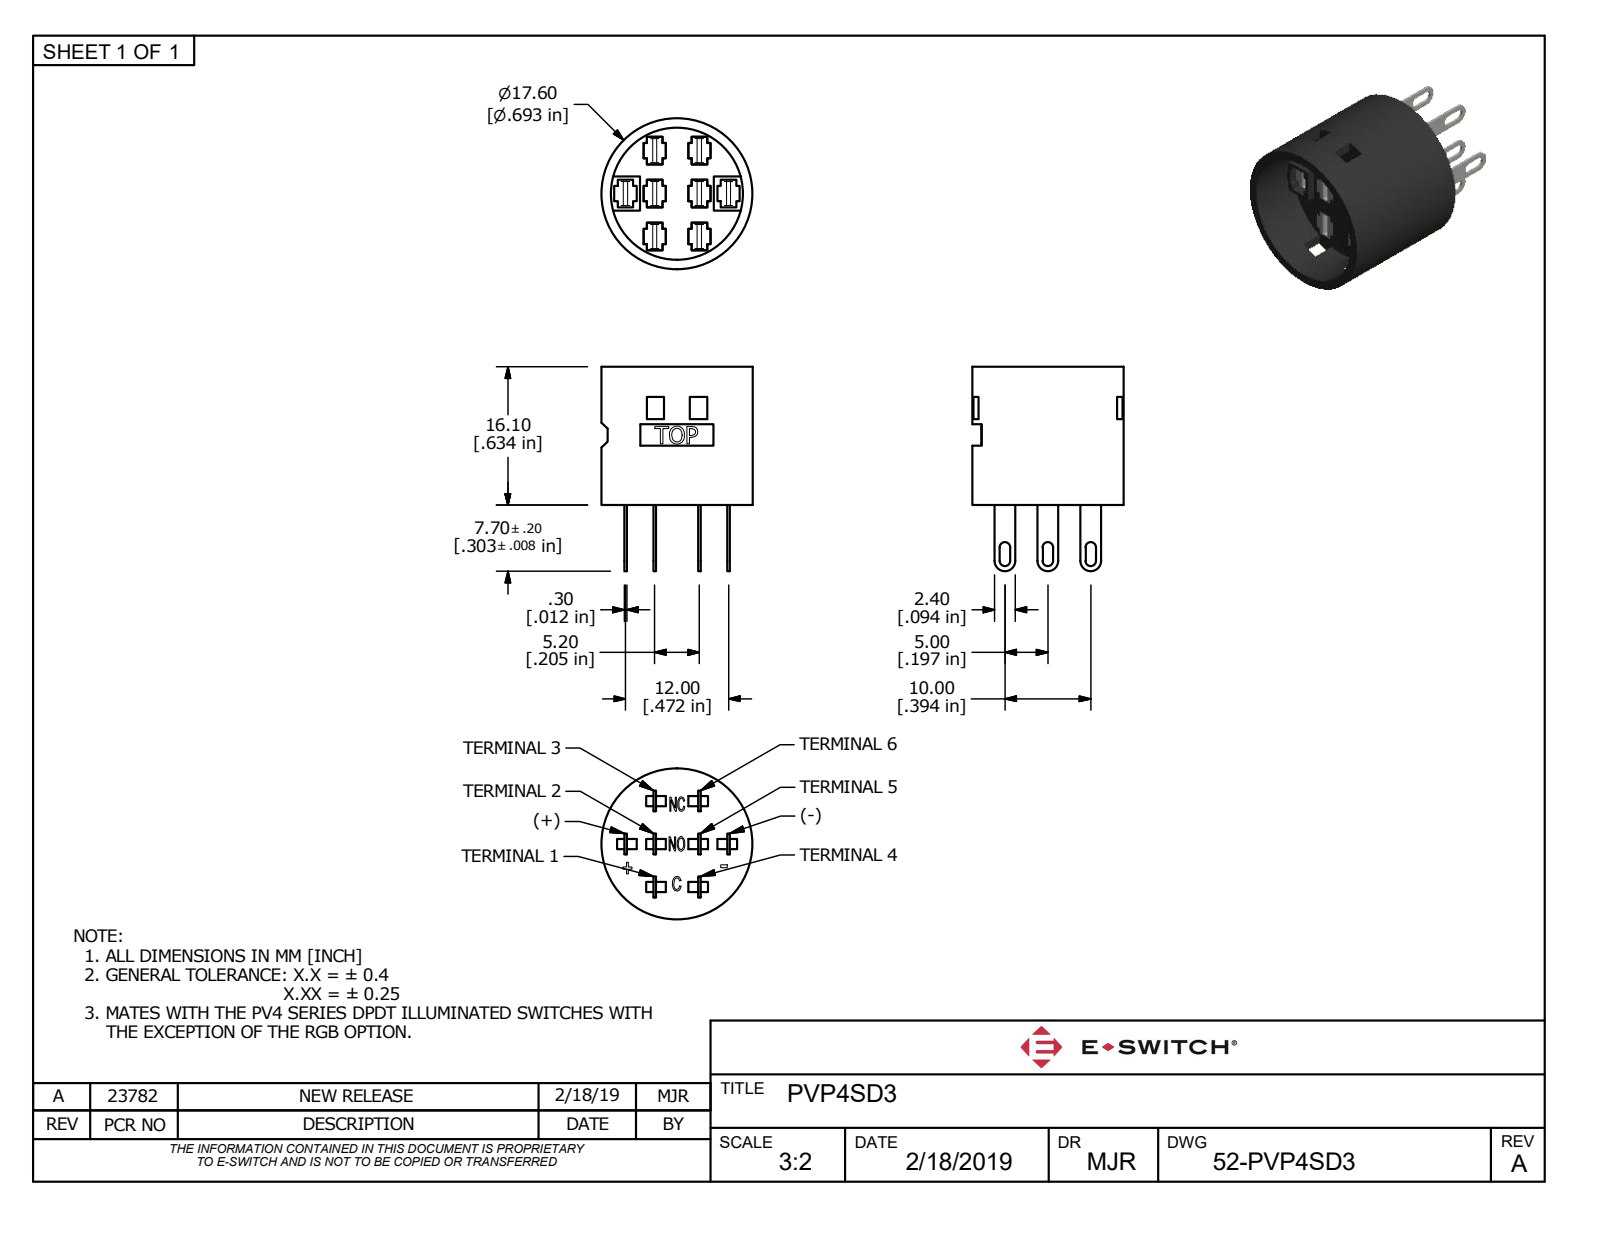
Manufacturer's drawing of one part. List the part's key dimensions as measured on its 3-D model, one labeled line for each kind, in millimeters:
Part name (STEP PRODUCT): PVP4SD3
STEP written by: Autodesk Inventor 2018 (AP242_MANAGED_MODEL_BASED_3D_ENGINEERING_MIM_LF)
Units: millimetres
Bodies: 1 solid, 565 faces (474 planar, 42 cylindrical, 49 other)
Overall size (bounding box): 23.9 × 17.6 × 17.6
Volume: 2 594 mm³ · Surface area: 2 723 mm²
Round holes (diameter × count): ⌀15.4 ×1
Round bosses / shafts (diameter × count): ⌀17.6 ×1
Partial cylindrical surfaces — rounded edges, fillets, slot ends (radius × count): R0.25 ×8, R0.6 ×6, R1.2 ×3
Main face-to-face distances: 0.4, 5.2, 8.6, 0.5, 4.8, 3.4, 3, 5.6, 5.1, 9.9
